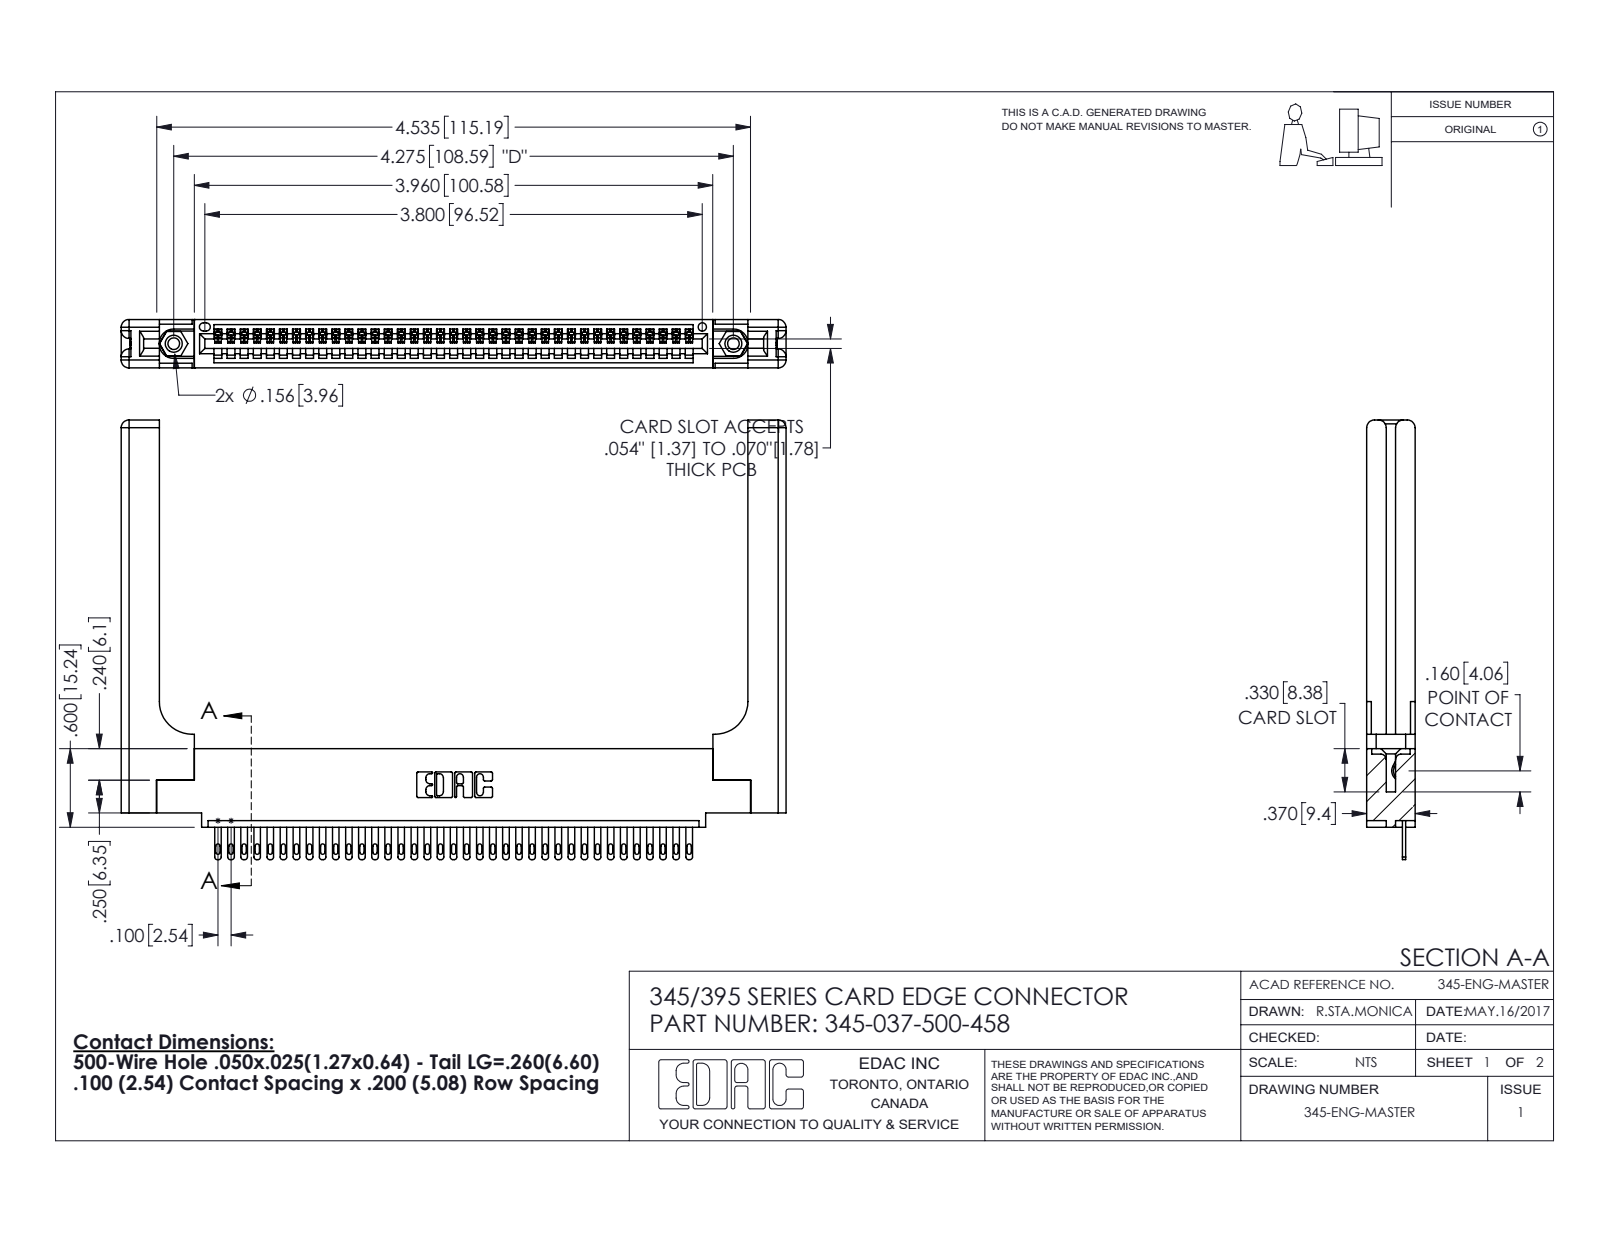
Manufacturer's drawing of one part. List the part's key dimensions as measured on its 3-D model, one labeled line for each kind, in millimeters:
Part name (STEP PRODUCT): 345-220-058_345-220-058; 345-250-001_345-250-001-102; 345-037-500-458; 345-292-001_345-293-100 (+1 more)
STEP written by: SolidWorks 2016 (CONFIG_CONTROL_DESIGN)
Units: millimetres
Bodies: 42 solids, 2384 faces (1490 planar, 834 cylindrical, 60 other)
Overall size (bounding box): 129 × 85.3 × 9.4
Volume: 20 660 mm³ · Surface area: 21 560 mm²
Round holes (diameter × count): ⌀2.3 ×2, ⌀3.2 ×2, ⌀4 ×2, ⌀1.6 ×1
Round bosses / shafts (diameter × count): ⌀3.9 ×2
Partial cylindrical surfaces — rounded edges, fillets, slot ends (radius × count): R0.2 ×74, R0.4 ×74, R0.5 ×74, R0.3 ×22, R1.5 ×16, R0.2 ×6, R0.8 ×6, R0.7 ×3
Main face-to-face distances: 1.8, 9.4, 7.6, 2.5, 6.9, 0.6, 5.1, 3.8, 3.8, 5.7
Hole centre spacings: 6.9, 102.6, 108.6
